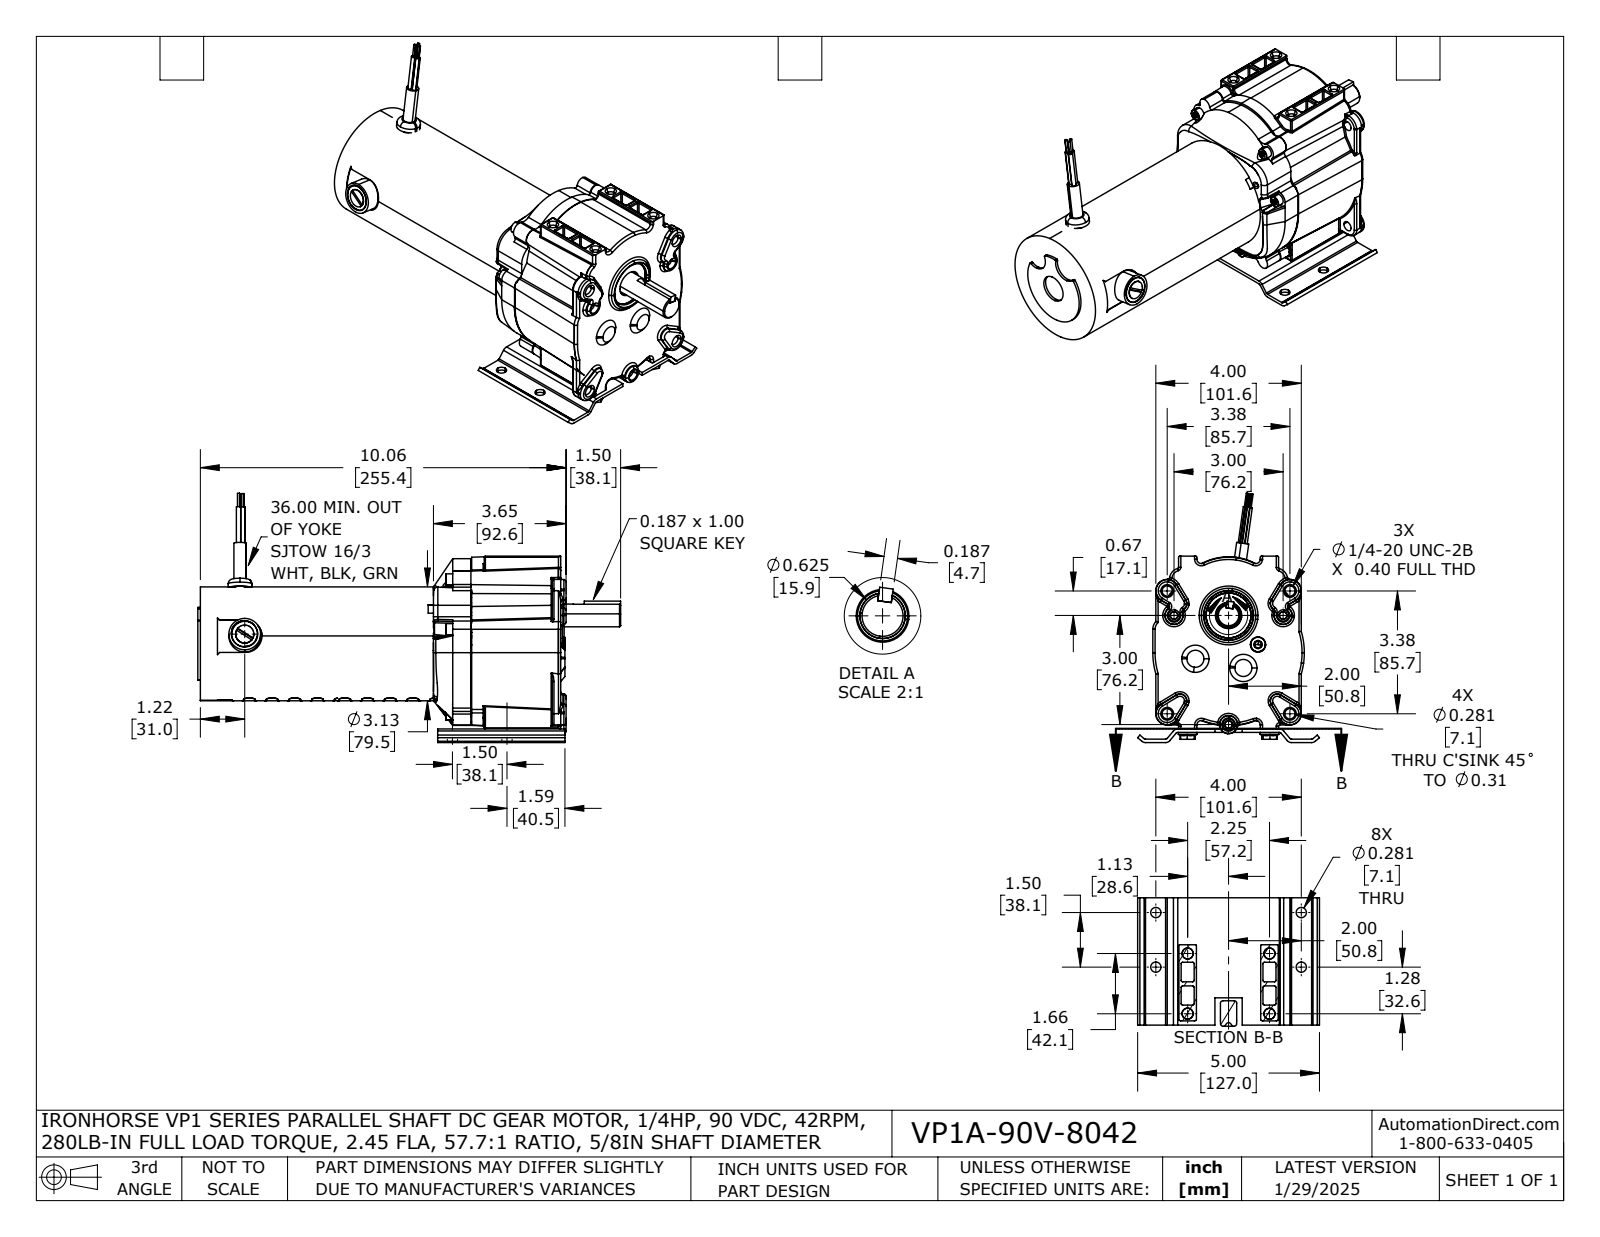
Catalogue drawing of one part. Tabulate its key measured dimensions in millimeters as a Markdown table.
| quantity | value |
| --- | --- |
| part name | VP1A-90V-8042 |
| STEP written by | SolidWorks 2024 (AUTOMOTIVE_DESIGN) |
| units | millimeters |
| bodies | 10 solids, 2472 faces (654 planar, 701 cylindrical, 1117 other) |
| overall size | 295.3 × 174.1 × 127 |
| volume | 1 621 000 mm³ |
| surface area | 222 800 mm² |
| round holes (diameter × count) | 7.1 × 12, 5.5 × 5, 4 × 3, 5.3 × 3, 3.4 × 2, 4.2 × 2, 5.2 × 2, 10.1 × 2, 17.5 × 2, 22.2 × 2, 19.1 × 1, 20.7 × 1 |
| round bosses / shafts (diameter × count) | 7.8 × 5, 4.8 × 5, 13 × 4, 7.6 × 4, 3 × 3, 1.5 × 3, 22.2 × 2, 18.6 × 2 |
| partial cylindrical surfaces (radius × count) | 0.8 × 52, 0.8 × 38, 1.6 × 23, 3 × 18, 4 × 18, 4.8 × 10, 3.8 × 9, 4.1 × 9 |
| main face-to-face distances | 2.4, 62.2, 88.9, 26.7, 239.8, 177.6, 150.9, 11.9, 177, 251.7 |
| hole center spacings | 38.1, 85.7, 43, 12.5, 17.7, 31.1, 36.2, 39.4 |
